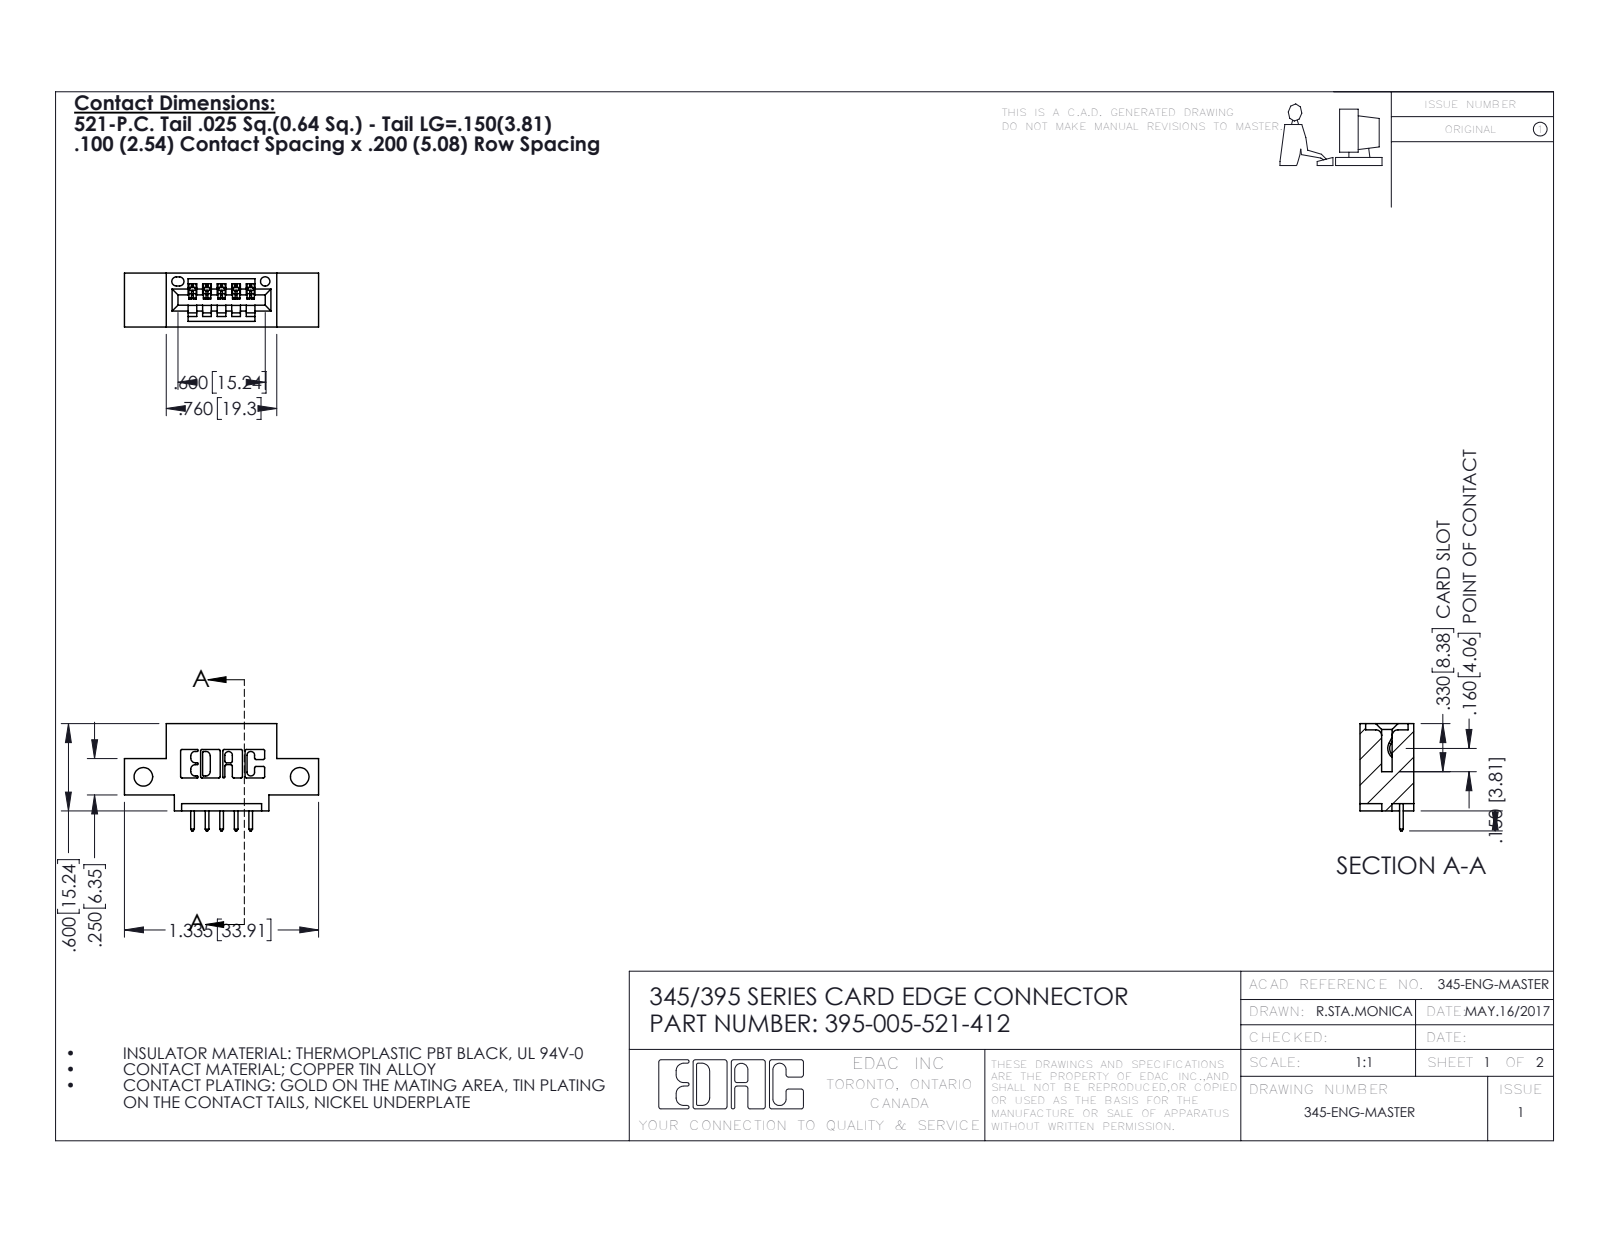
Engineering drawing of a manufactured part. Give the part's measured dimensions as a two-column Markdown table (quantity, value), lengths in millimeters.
| quantity | value |
| --- | --- |
| part name | 395-005-521-412; 345-292-001_345-293-121; 345 Part_0.110 Offset - Side Mount |
| STEP written by | SolidWorks 2016 (CONFIG_CONTROL_DESIGN) |
| units | millimeters |
| bodies | 6 solids, 420 faces (284 planar, 136 cylindrical, 0 other) |
| overall size | 33.9 × 18.7 × 9.4 |
| volume | 2 740 mm³ |
| surface area | 3 026 mm² |
| round holes (diameter × count) | 3.3 × 2, 1.6 × 1 |
| partial cylindrical surfaces (radius × count) | 0.3 × 22, 0.2 × 10, 0.3 × 10, 0.2 × 6, 0.8 × 6, 0.7 × 3, 0.8 × 2, 1 × 2 |
| main face-to-face distances | 5.1, 9.4, 7.6, 1.8, 2.5, 6.4, 0.6, 2.5, 6.9, 1.5 |
| hole center spacings | 27.3 |
